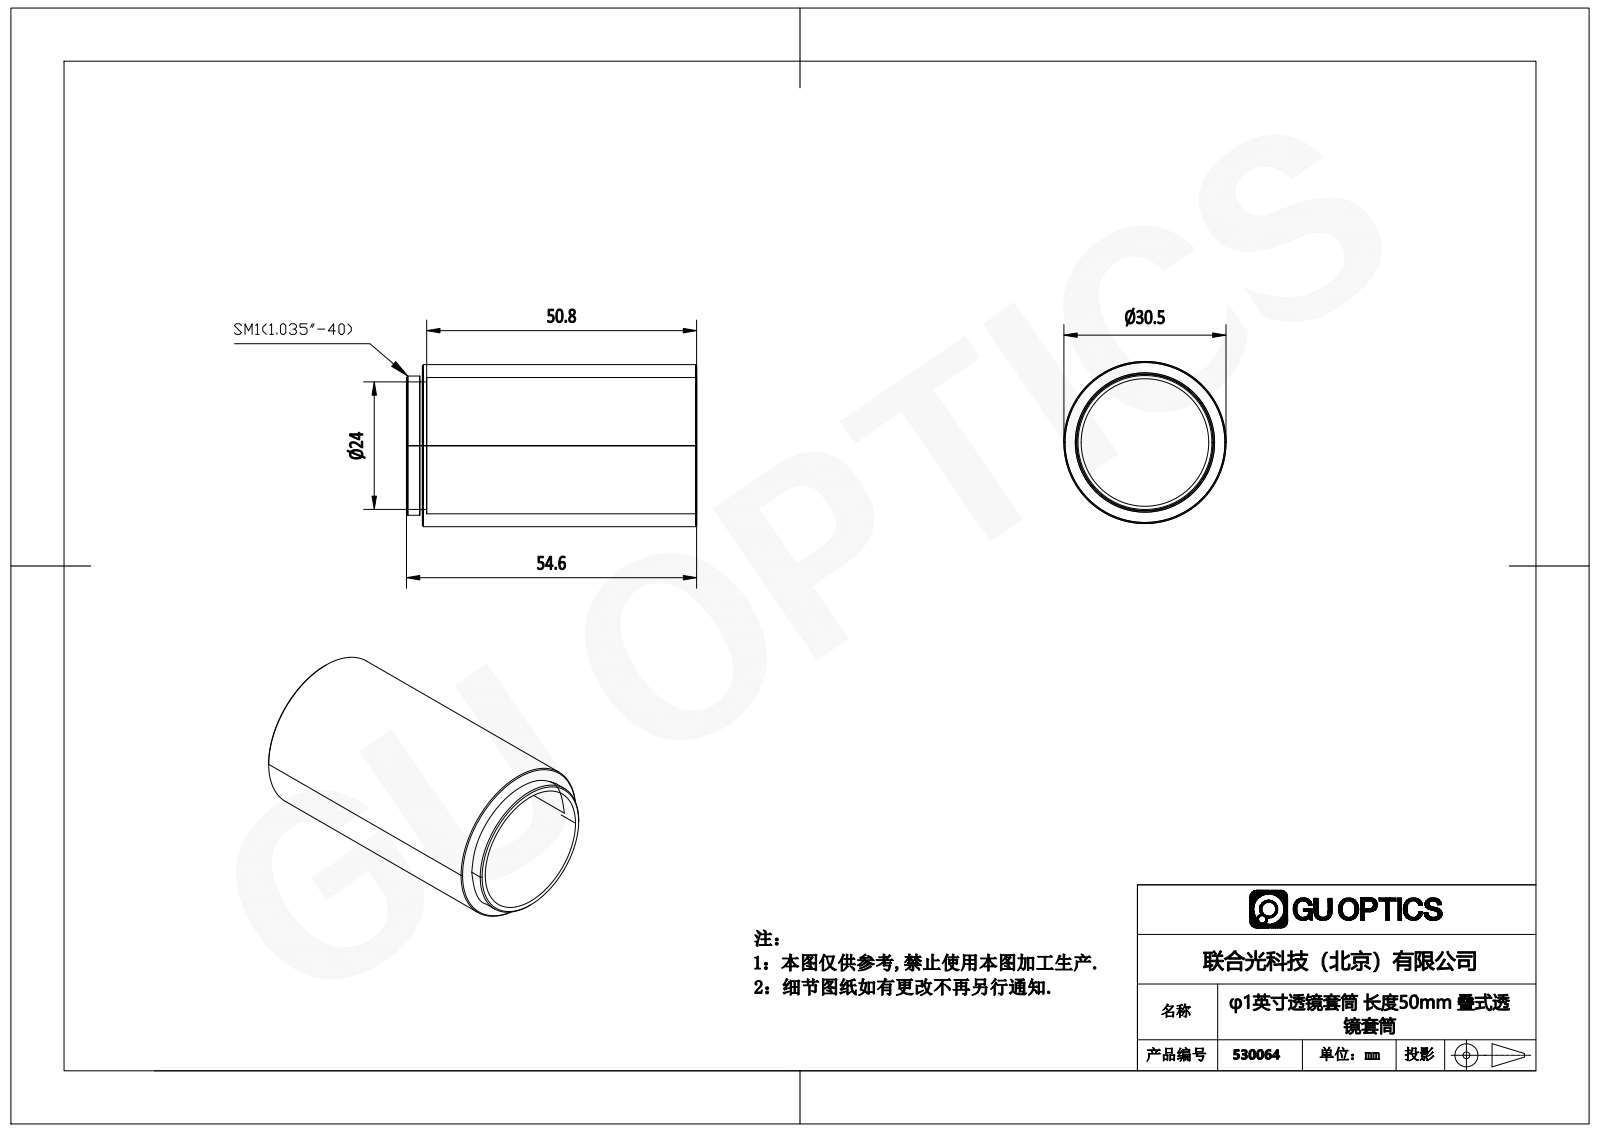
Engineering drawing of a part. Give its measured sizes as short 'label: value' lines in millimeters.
written by: SolidWorks 2018 (AUTOMOTIVE_DESIGN)
unit: mm
bodies: 0 solids, 34 faces (11 planar, 12 cylindrical, 11 other)
size: 54.6 × 30.5 × 30.5
holes: 1× ⌀23.01, 1× ⌀24, 1× ⌀25.65
bosses: 1× ⌀30.5, 1× ⌀26.2, 1× ⌀25.2
face distances: 51.6, 51.43, 54.6, 54.43, 3, 0.87, 0.7, 50.73, 53.73, 1
